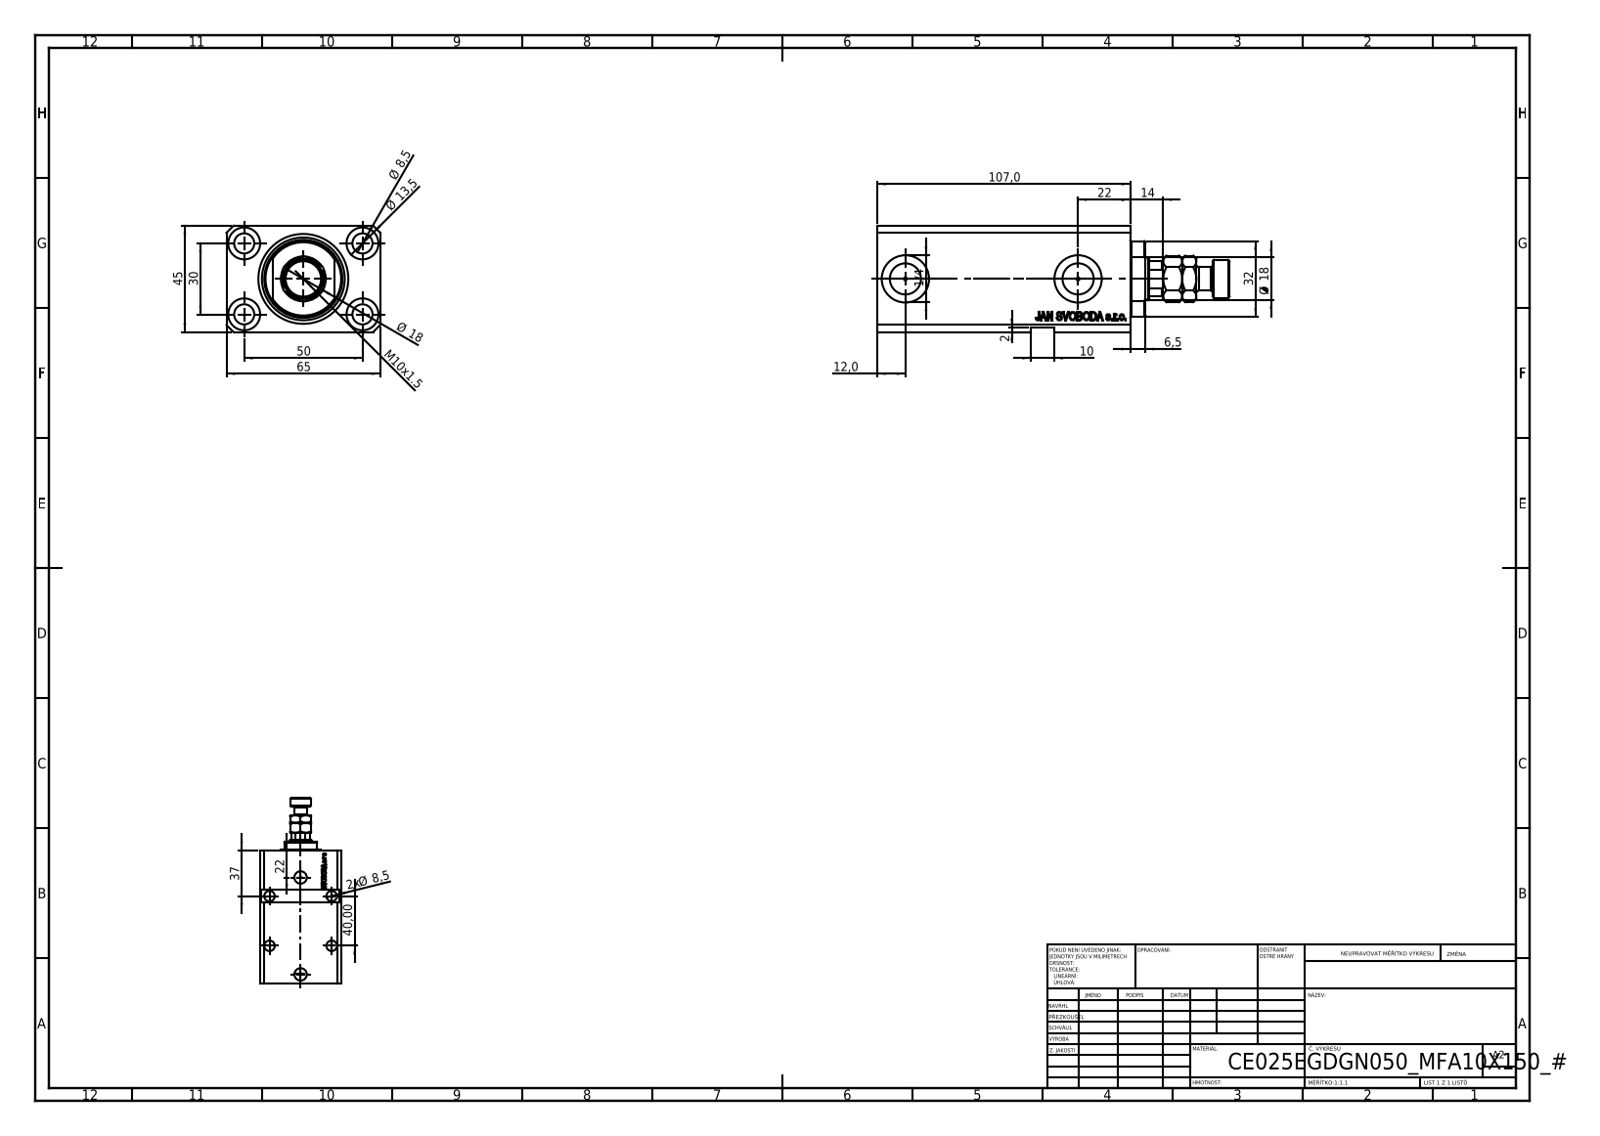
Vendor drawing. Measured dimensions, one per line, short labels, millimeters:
name: V250CE_E_Body; V250CE_VC_E; V250CE_C_VCP; MFA
written by: SolidWorks 2019 (CONFIG_CONTROL_DESIGN)
unit: mm
bodies: 4 solids, 985 faces (455 planar, 120 cylindrical, 410 other)
size: 149 × 65 × 45
volume: 263 363 mm³; area: 70 127 mm²
holes: 9× ⌀8.5, 4× ⌀1.25, 4× ⌀13.5, 2× ⌀10, 2× ⌀13.16, 2× ⌀20, 1× ⌀18, 1× ⌀25, 1× ⌀38
bosses: 1× ⌀16, 1× ⌀10
rounds: 1× R8.5, 1× R16
face distances: 45, 65, 14, 93, 107, 6.9, 86.1, 100.1, 28, 43
hole spacings: 29.15, 50, 30, 33.61, 33.97, 40, 58.31, 60.42
